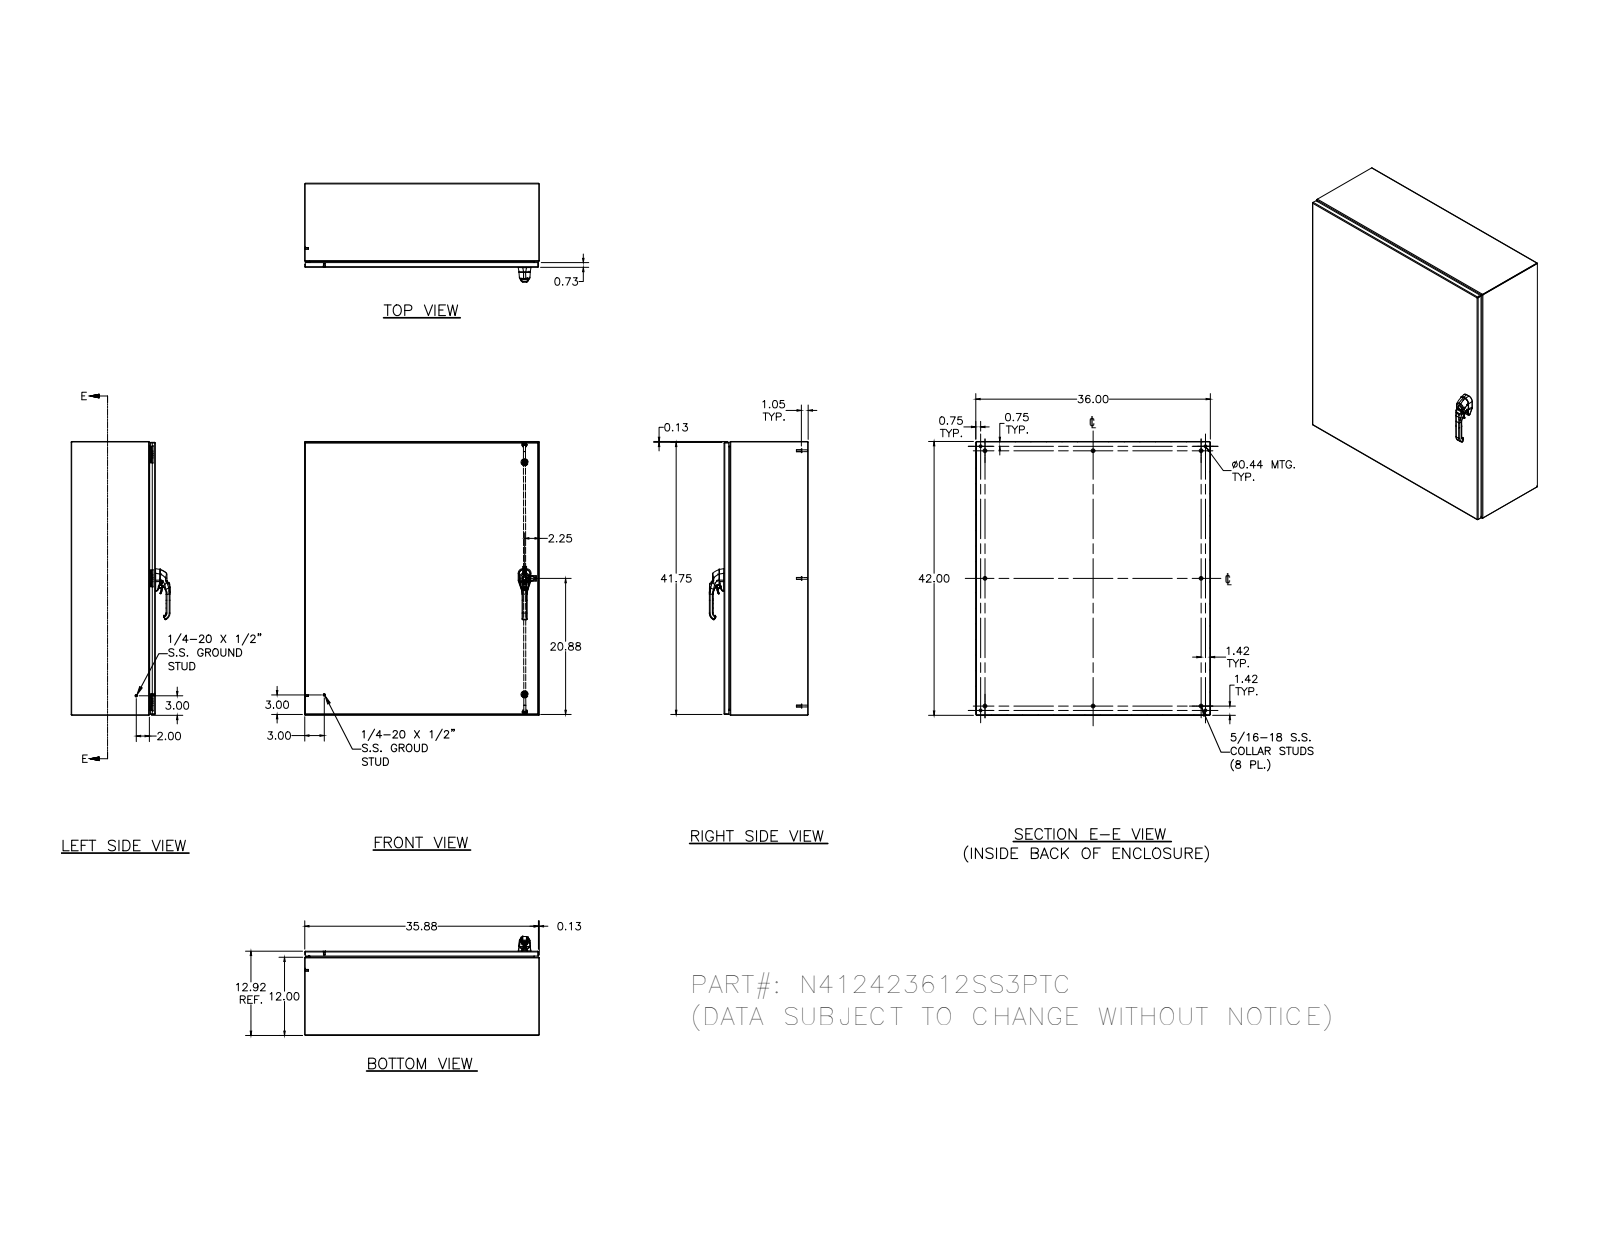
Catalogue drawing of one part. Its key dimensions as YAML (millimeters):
part_name: "N412423612SS3PTC; N412423612SS3PTCBTB; N4124212SS3PTCLS; N4124212SS3PTCRS (+8 more)"
step_written_by: "Autodesk Inventor 2011 (AUTOMOTIVE_DESIGN)"
units: millimeters
bodies: {solids: 78, faces: 3550, planar: 1203, cylindrical: 1297, other: 1050}
overall_size: [1066.8, 914.4, 385.2]
volume: 6502000
surface_area: 6844000
round_holes:
  - {diameter: 2.4, count: 6}
  - {diameter: 3.9, count: 6}
  - {diameter: 4.2, count: 6}
  - {diameter: 4.4, count: 6}
  - {diameter: 4.7, count: 6}
  - {diameter: 4.2, count: 5}
  - {diameter: 5, count: 4}
  - {diameter: 11.1, count: 4}
  - {diameter: 4, count: 3}
  - {diameter: 5.4, count: 3}
  - {diameter: 2.7, count: 2}
  - {diameter: 4.1, count: 2}
round_bosses_or_shafts:
  - {diameter: 6.4, count: 14}
  - {diameter: 14.3, count: 8}
  - {diameter: 7.6, count: 8}
  - {diameter: 7, count: 8}
  - {diameter: 9.1, count: 6}
  - {diameter: 8.1, count: 6}
  - {diameter: 6.5, count: 6}
  - {diameter: 6, count: 6}
partial_cylinders:
  - {radius: 0.5, count: 186}
  - {radius: 0.3, count: 100}
  - {radius: 1.3, count: 38}
  - {radius: 0.8, count: 32}
  - {radius: 0.4, count: 26}
  - {radius: 3.2, count: 24}
  - {radius: 0.5, count: 23}
  - {radius: 3, count: 23}
face_to_face_distances: [1.9, 326.2, 324.3, 328.1, 912.5, 1064.9, 910.6, 914.4, 1063, 1066.8]
hole_center_spacings: [482.6, 965.2, 482.8, 12.7, 16.7, 16.8, 33.2, 33.3]
